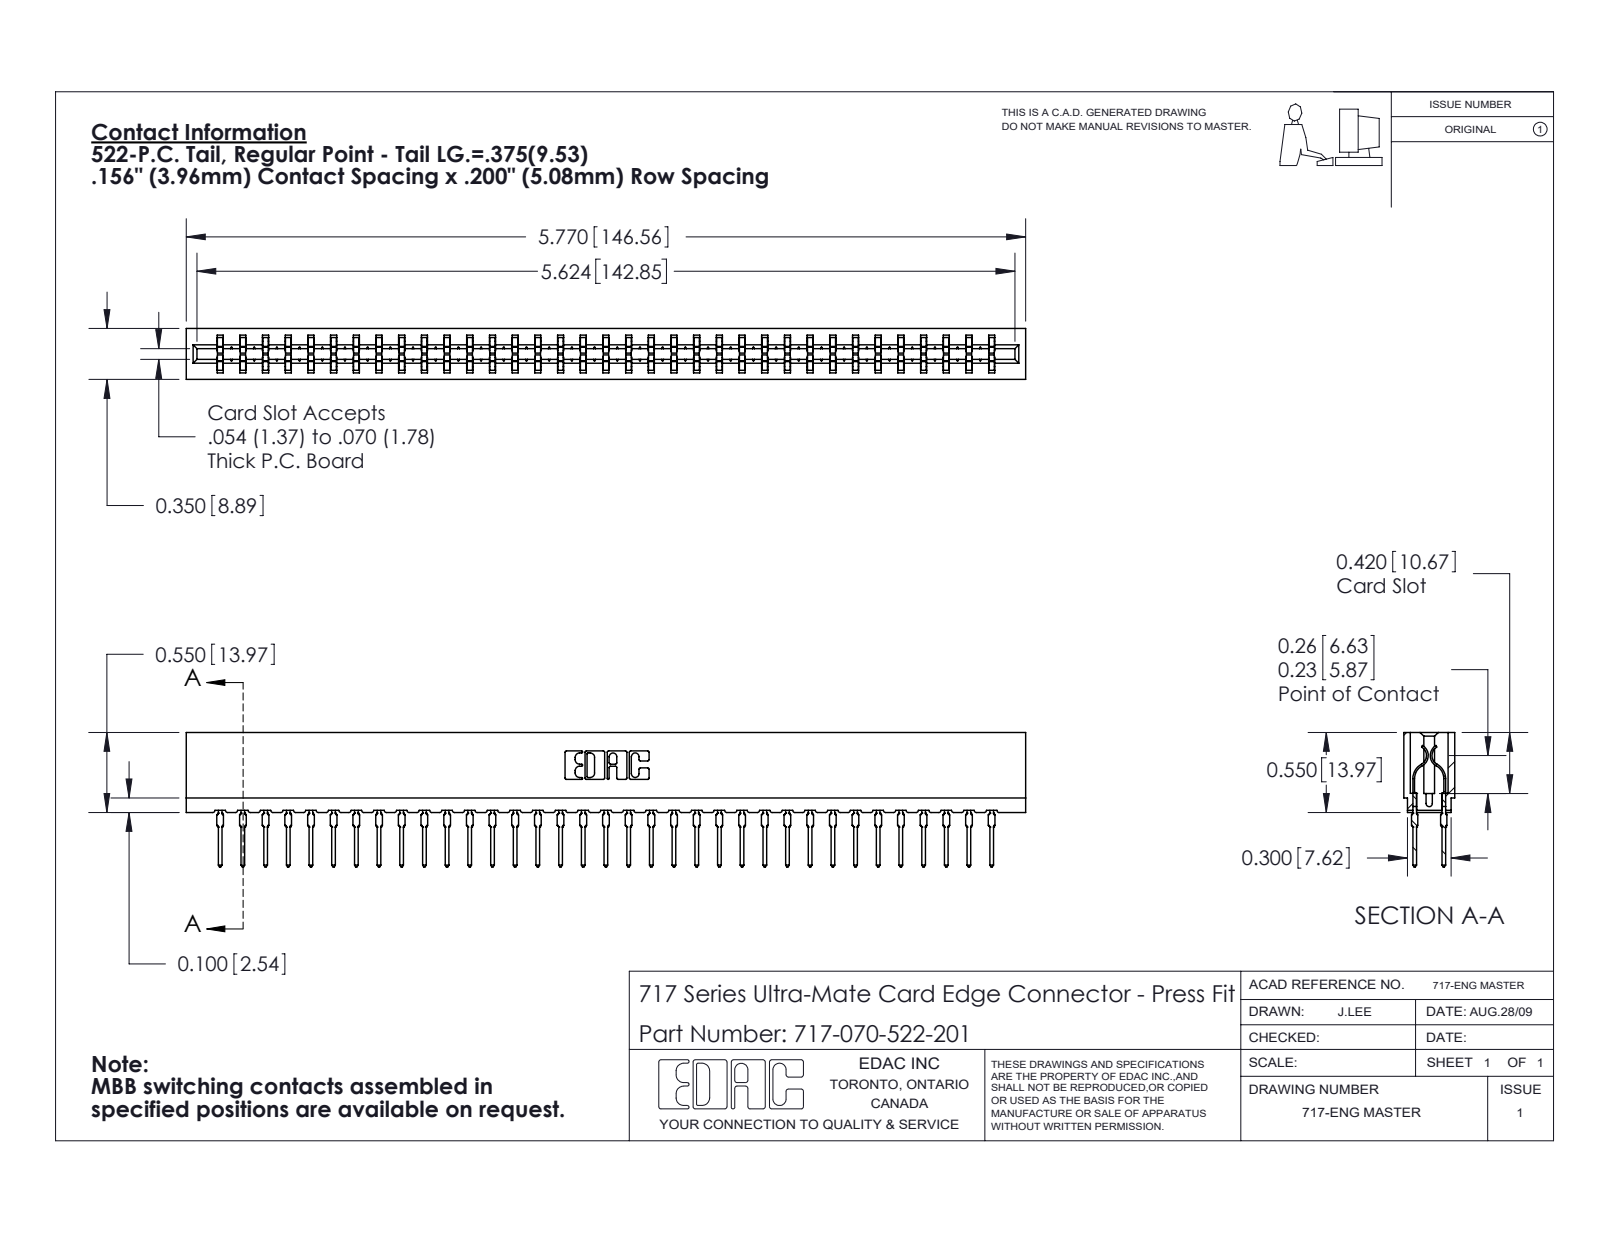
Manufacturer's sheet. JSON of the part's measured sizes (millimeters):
{"part_name": "717-070-522-201; 745-292-001_522; 717 Part_Insulator Option - 06", "step_written_by": "SolidWorks 2020 (CONFIG_CONTROL_DESIGN)", "units": "millimeters", "bodies": {"solids": 71, "faces": 6394, "planar": 3309, "cylindrical": 1265, "other": 1820}, "overall_size": [146.6, 23.5, 8.9], "volume_mm3": 12800, "surface_area_mm2": 19770, "partial_cylinders_radius": [[0.5, 140], [0.4, 70], [0.3, 22], [0.1, 8], [0.3, 8], [0.2, 6], [0.8, 6], [0.7, 3]], "face_to_face_distances": [5.4, 3.5, 8.9, 1.6, 7.3, 1.9, 3.8, 1.9, 1.1, 7.7]}
